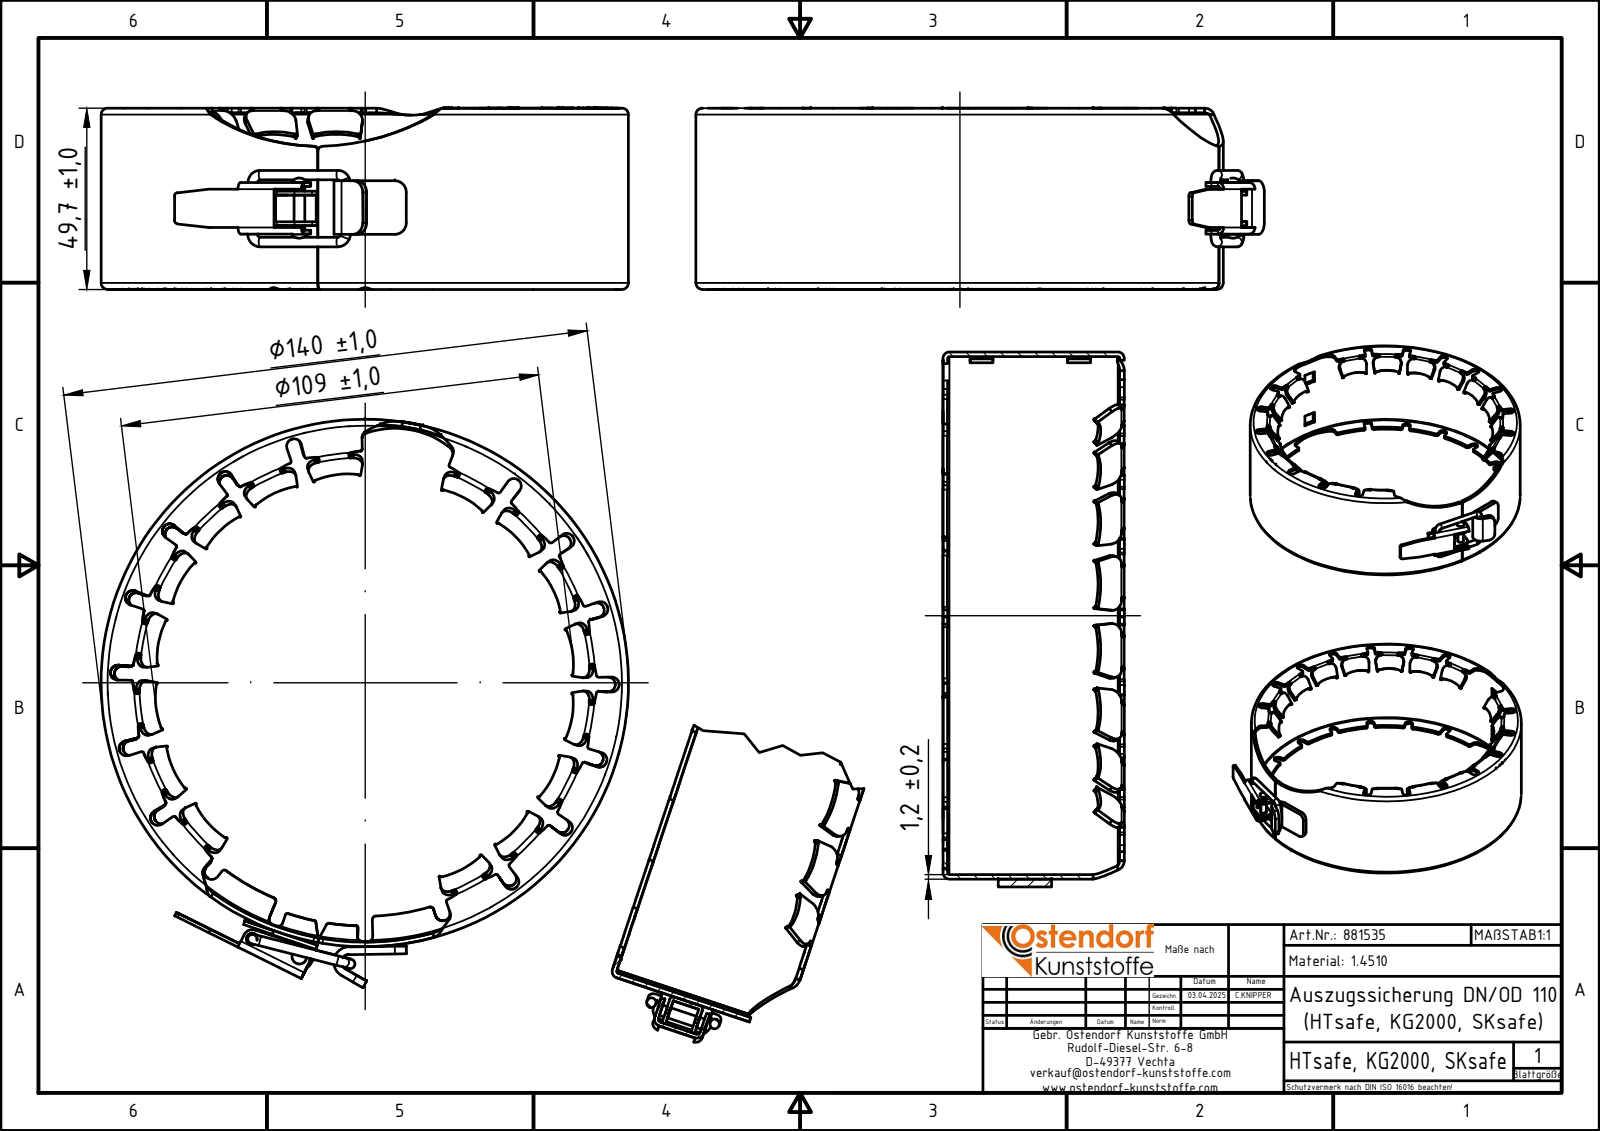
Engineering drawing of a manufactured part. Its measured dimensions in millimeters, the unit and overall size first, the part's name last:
Units: millimetres
Overall size (bounding box): 148.74 × 138 × 47.43
Round holes (diameter × count): ⌀3 ×3, ⌀135.6 ×1
Round bosses / shafts (diameter × count): ⌀2.5 ×3, ⌀138 ×1, ⌀2.8 ×1
Partial cylindrical surfaces — rounded edges, fillets, slot ends (radius × count): R3.61 ×7, R3.62 ×7, R3 ×5, R1 ×4, R0.74 ×2, R1.74 ×2, R3.5 ×2, R3.61 ×2
Main face-to-face distances: 1, 2, 12.47, 0.99, 8, 10.22, 2.25, 2.22, 10.25, 13.47
Hole centre spacings: 5, 8.06, 13.06, 73.14, 73.16, 73.66
Volume: 32 512 mm³ · Surface area: 56 366 mm²
Bodies: 6 solids, 1087 faces (134 planar, 87 cylindrical, 866 other)
Part name (STEP PRODUCT): 881535z
STEP written by: Autodesk Inventor 2024 (AUTOMOTIVE_DESIGN)
